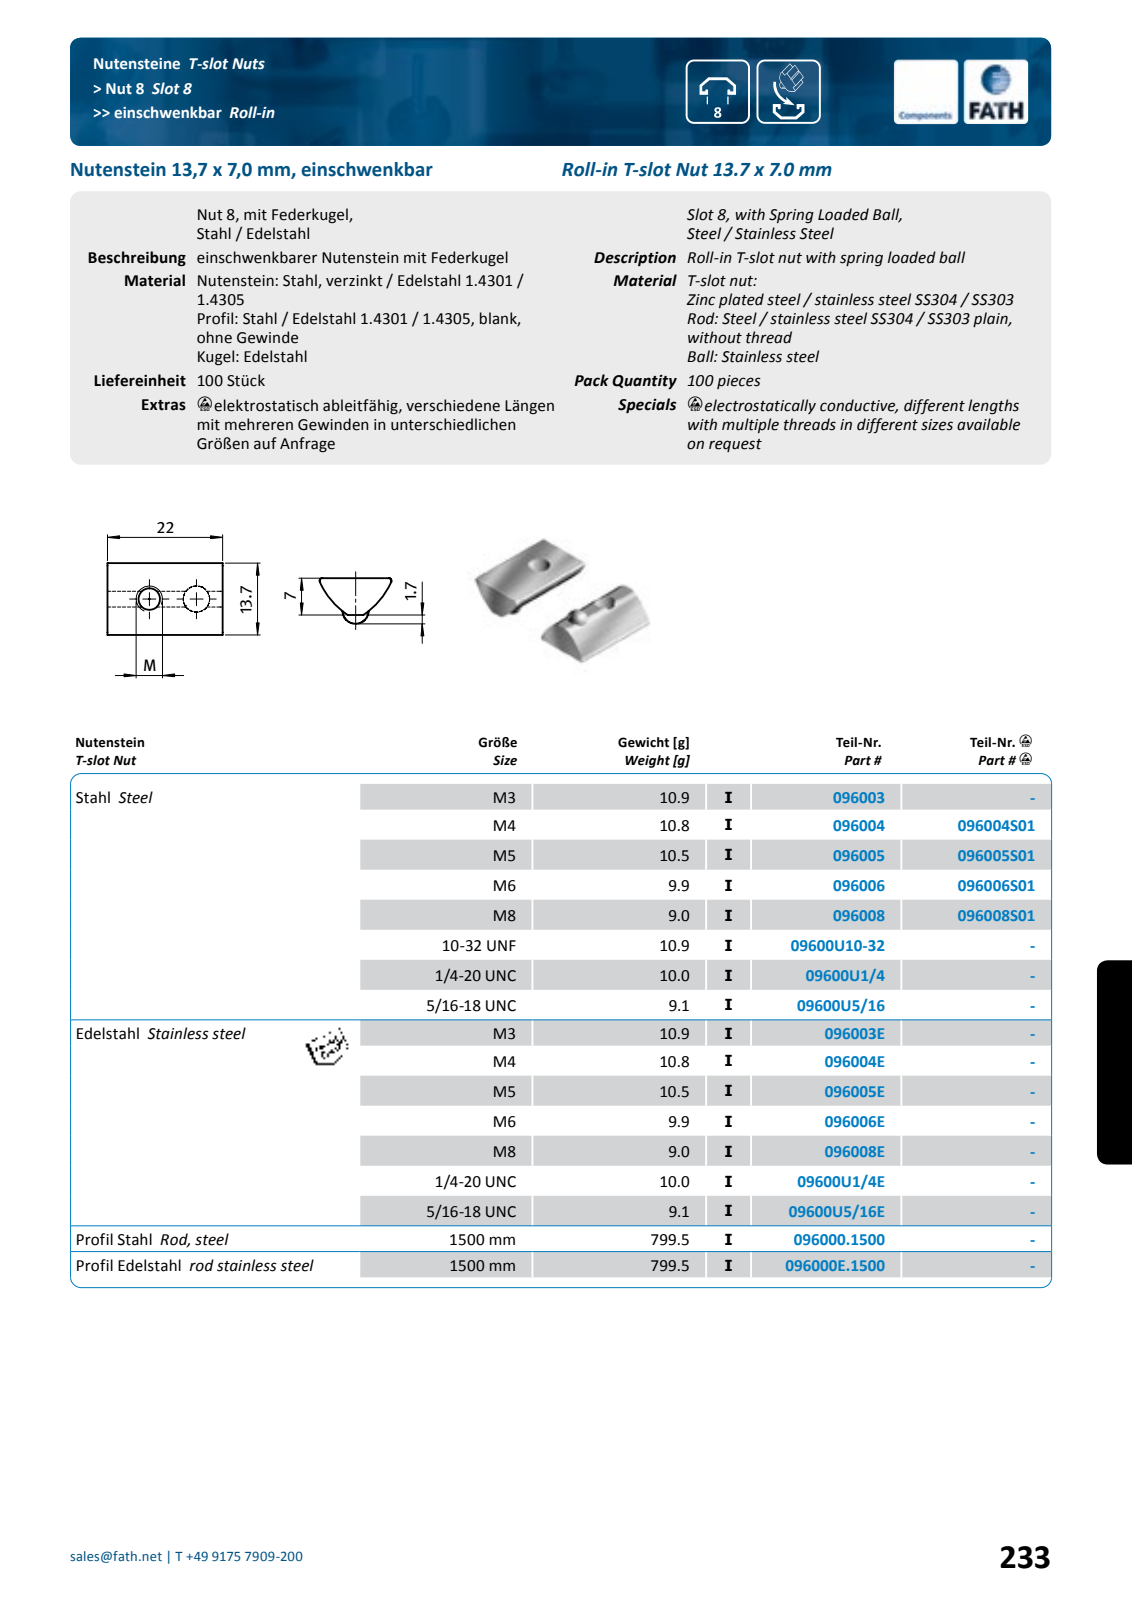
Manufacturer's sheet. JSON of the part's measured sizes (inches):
{"part_name": "fath_09600u1-4", "step_written_by": "Spatial InterOp 3D (automotive_design)", "units": "inches", "bodies": {"solids": 1, "faces": 27, "planar": 7, "cylindrical": 10, "other": 10}, "overall_size": [0.866, 0.539, 0.276], "volume_in3": 0.075, "surface_area_in2": 1.603, "round_holes": [[0.197, 1], [0.201, 1]], "partial_cylinders_radius": [[0.02, 2], [0.591, 2]], "face_to_face_distances": [0.866, 0.276, 0.272], "hole_center_spacings": [0.413]}
